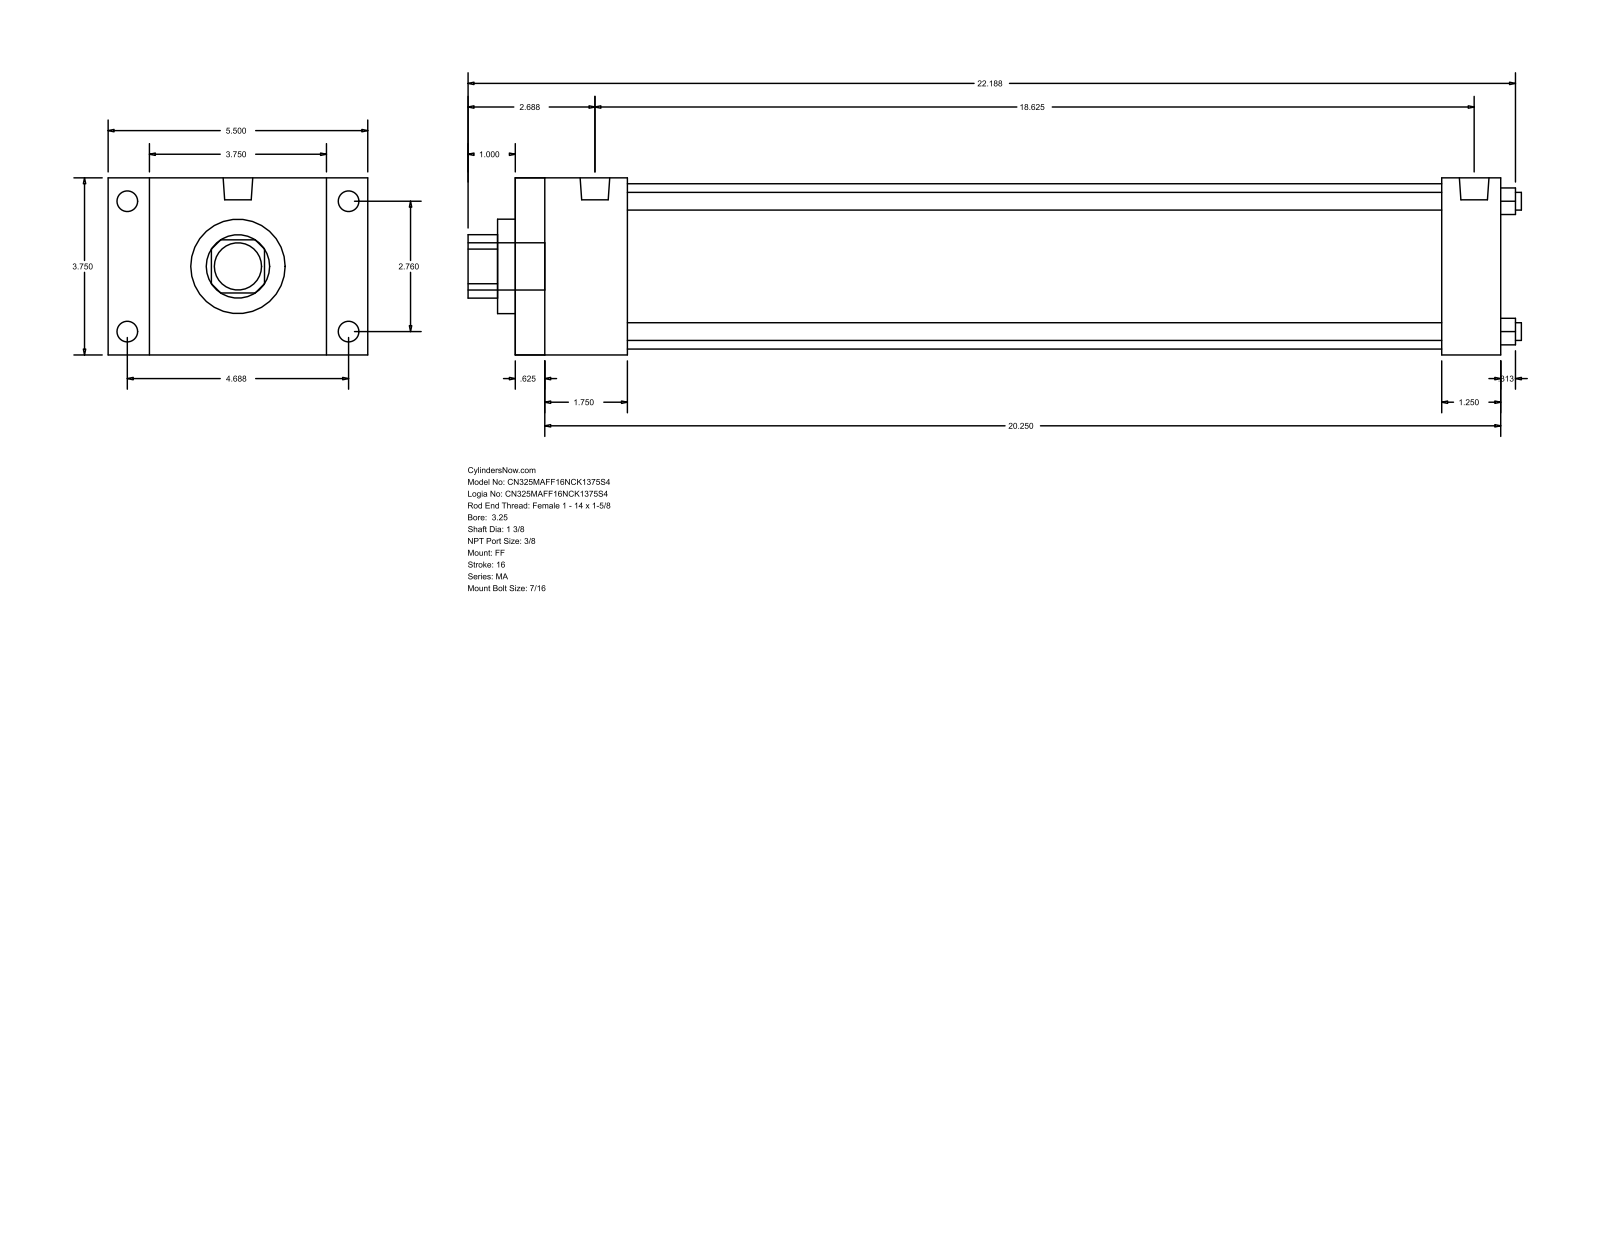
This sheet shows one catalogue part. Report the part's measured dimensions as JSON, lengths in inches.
{"part_name": "MA_FF__0325_1.375", "step_written_by": "GSSL Pune (CONFIG_CONTROL_DESIGN)", "units": "inches", "bodies": {"solids": 0, "faces": 92, "planar": 64, "cylindrical": 28, "other": 0}, "overall_size": [22.313, 5.5, 3.75], "round_holes": [[0.375, 4], [1.375, 1], [2, 1], [3.5, 1]], "round_bosses_or_shafts": [[0.437, 8], [0.627, 2], [1, 1]], "partial_cylinders_radius": [[0.672, 1]], "face_to_face_distances": [3.75, 20.875, 0.625, 20.25, 0.875, 4.625, 2.375, 19.625, 1.75, 19], "hole_center_spacings": [1.952, 2.76, 3.903]}
